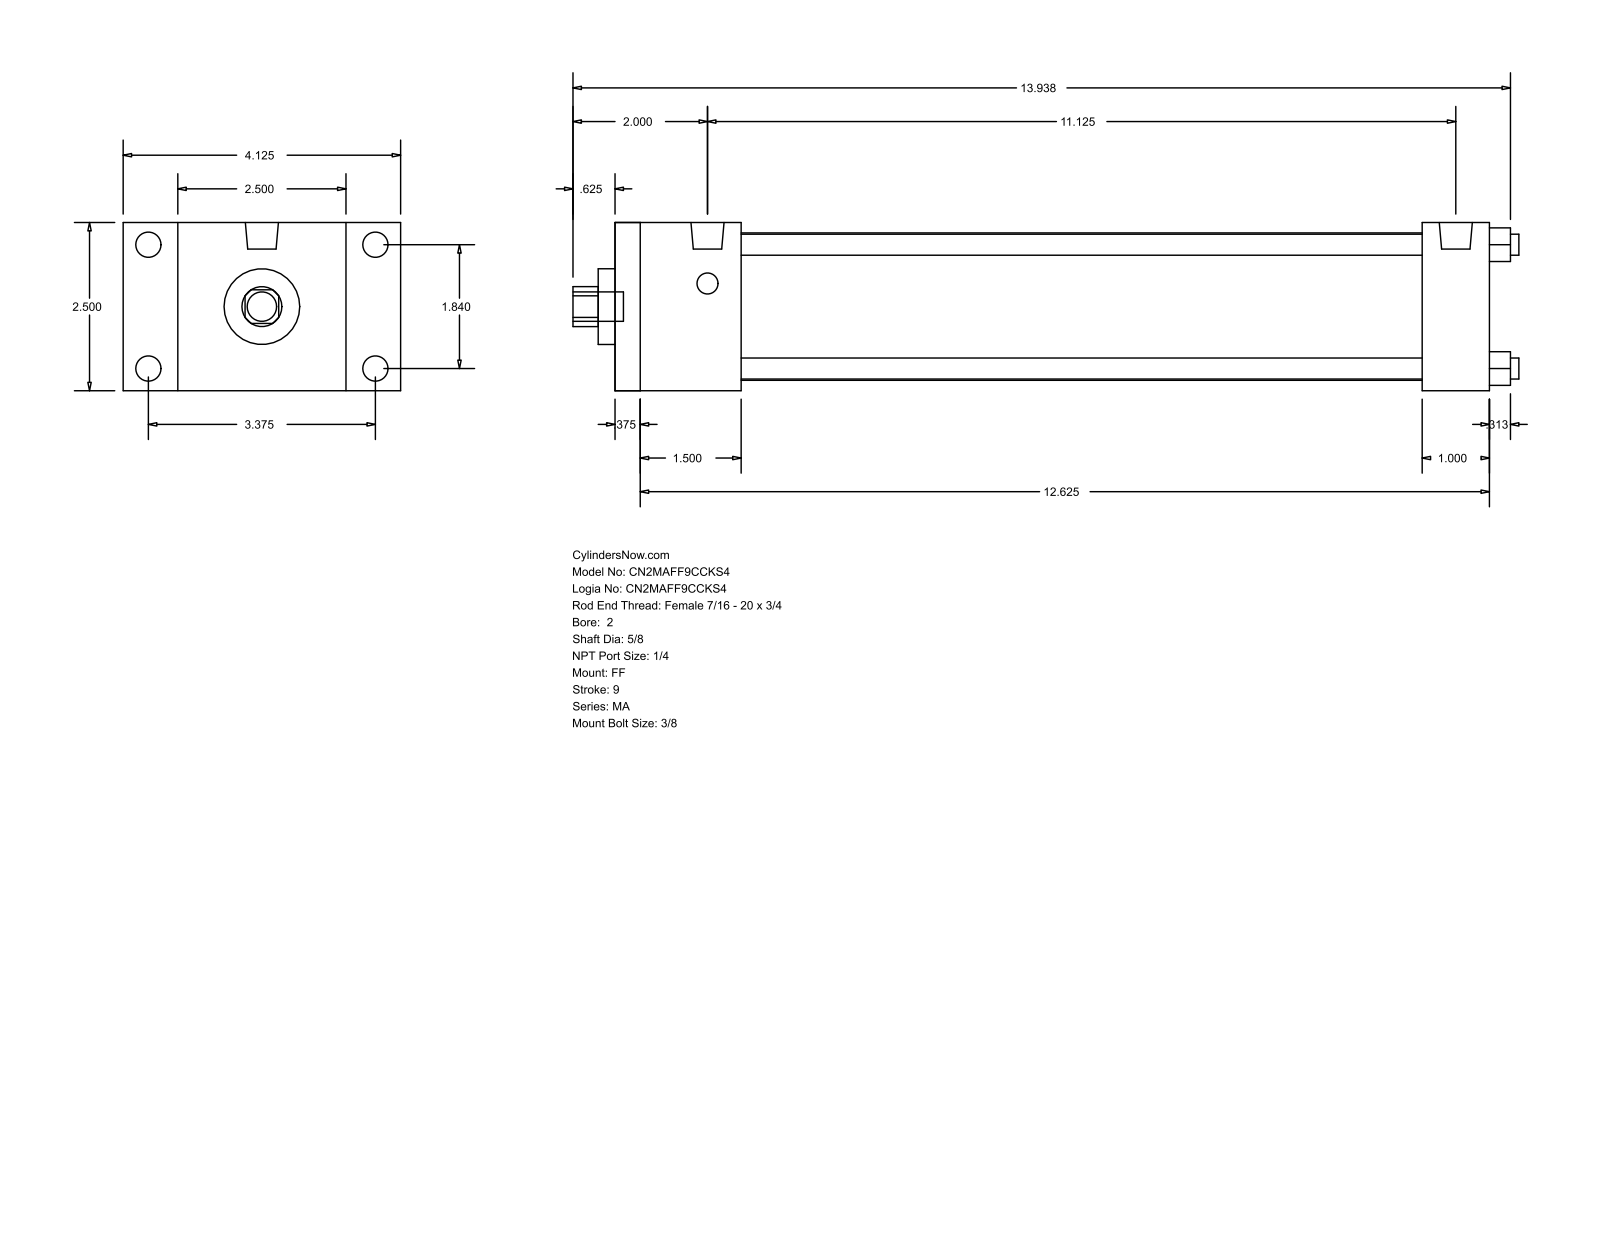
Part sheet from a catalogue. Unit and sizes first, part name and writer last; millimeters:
Units: millimetres
Overall size (bounding box): 357.19 × 104.78 × 63.5
Round holes (diameter × count): ⌀7.94 ×4, ⌀15.88 ×1, ⌀28.57 ×1, ⌀55.63 ×1
Round bosses / shafts (diameter × count): ⌀9.53 ×4, ⌀7.94 ×4, ⌀12.49 ×2, ⌀11.11 ×1
Partial cylindrical surfaces — rounded edges, fillets, slot ends (radius × count): R7.54 ×1
Main face-to-face distances: 63.5, 330.19, 9.52, 320.67, 38.1, 47.62, 304.8, 295.28, 257.18, 282.57
Hole centre spacings: 33.05, 46.74, 66.1
Bodies: 0 solids, 92 faces (64 planar, 28 cylindrical, 0 other)
Part name (STEP PRODUCT): MA_FF__0200_0.625
STEP written by: GSSL Pune (CONFIG_CONTROL_DESIGN)
